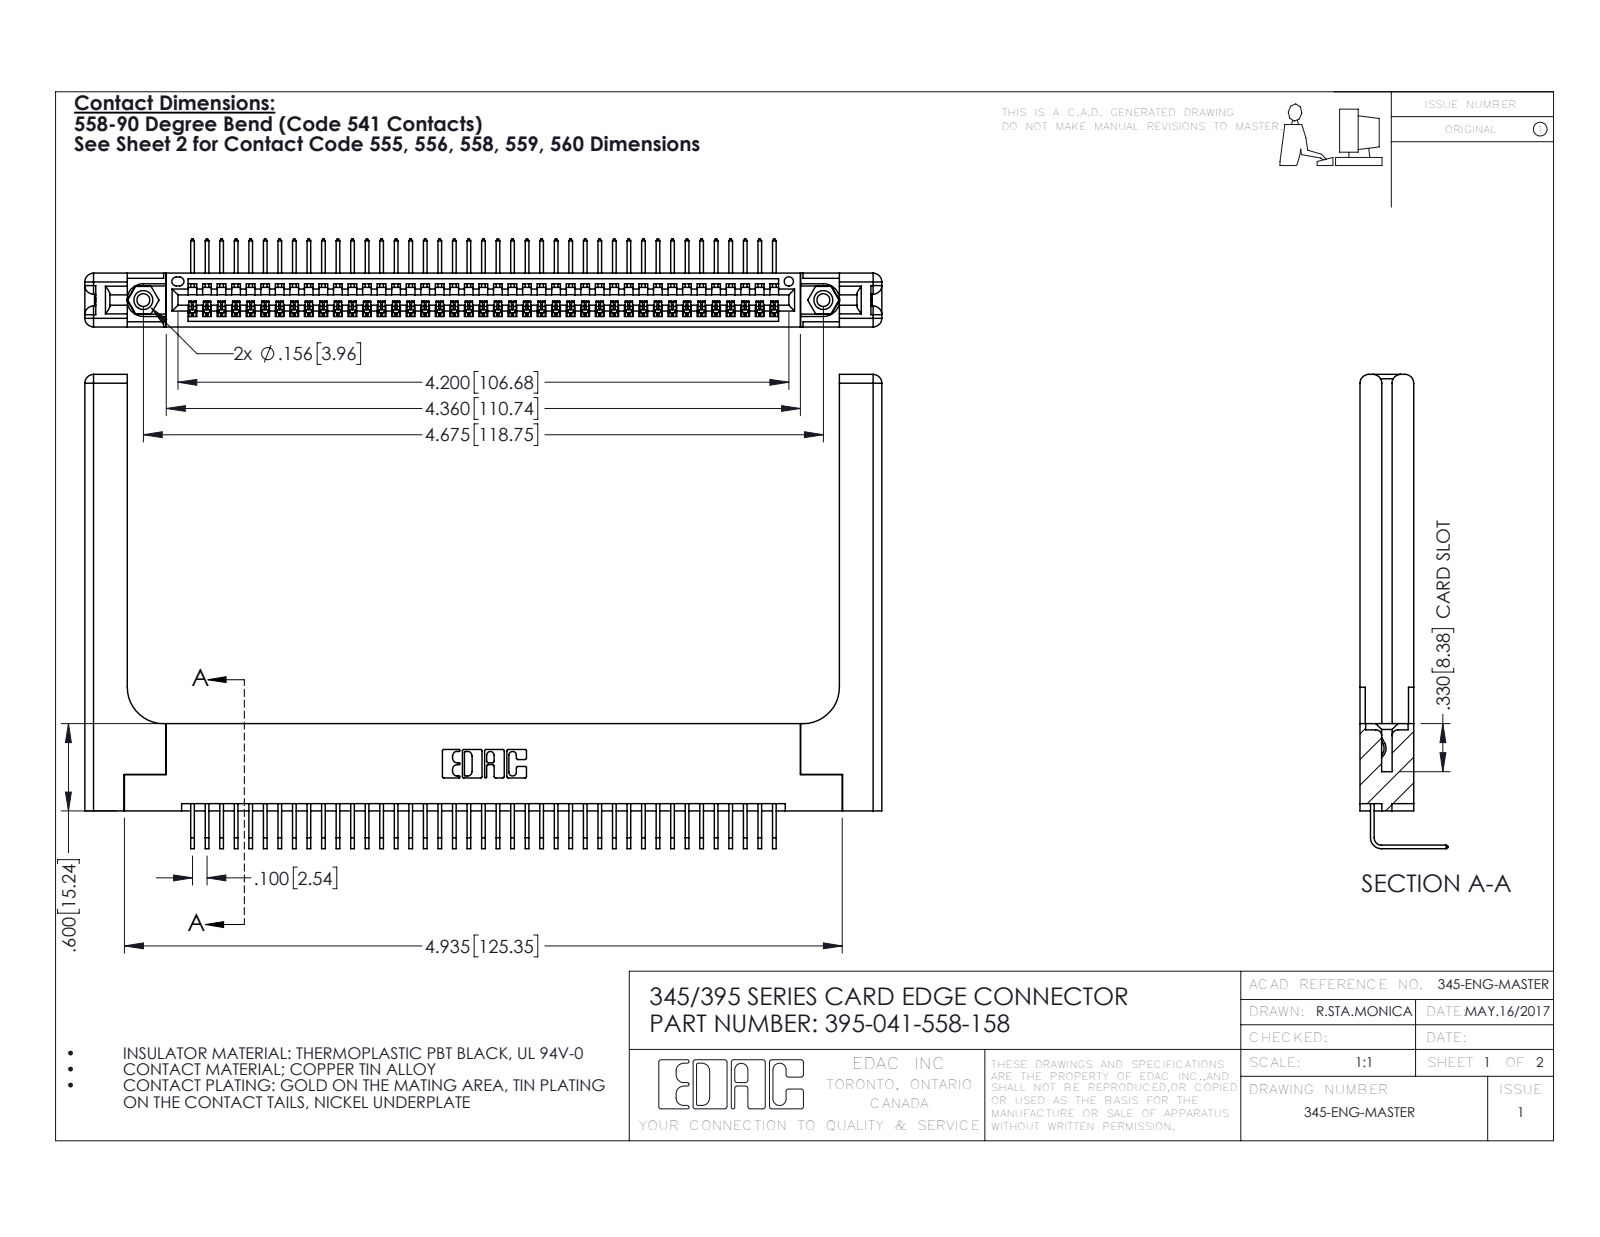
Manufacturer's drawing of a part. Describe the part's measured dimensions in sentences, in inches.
The part is named "395-041-558-158; 345-292-001_558 Tail - 2; 345-220-058_345-220-058; 345-250-001_345-250-001-102 (+1 more)". Its 3-D file was written by "SolidWorks 2016 (CONFIG_CONTROL_DESIGN)". It is 46 solids with 2842 faces: 1950 planar, 832 cylindrical and 60 other. Overall it measures 5.479 by 3.259 by 0.605 inches. Its volume is 1.333 cubic inches and its surface area 36.94 square inches. Round holes: 2 of diameter 0.089, 2 of diameter 0.125, 2 of diameter 0.156, 1 of diameter 0.064. Round bosses or shafts: 2 of diameter 0.155. Partial cylindrical surfaces (rounded edges, fillets, slot ends): 82 of radius 0.006, 22 of radius 0.01, 16 of radius 0.06, 6 of radius 0.007, 6 of radius 0.031, 3 of radius 0.026, 2 of radius 0.03, 2 of radius 0.031. The main face-to-face distances are 0.37, 0.072, 0.298, 0.2, 0.098, 0.272, 0.025, 0.148, 0.15, 0.225. The hole center spacings are 0.27, 4.439, 4.675.
